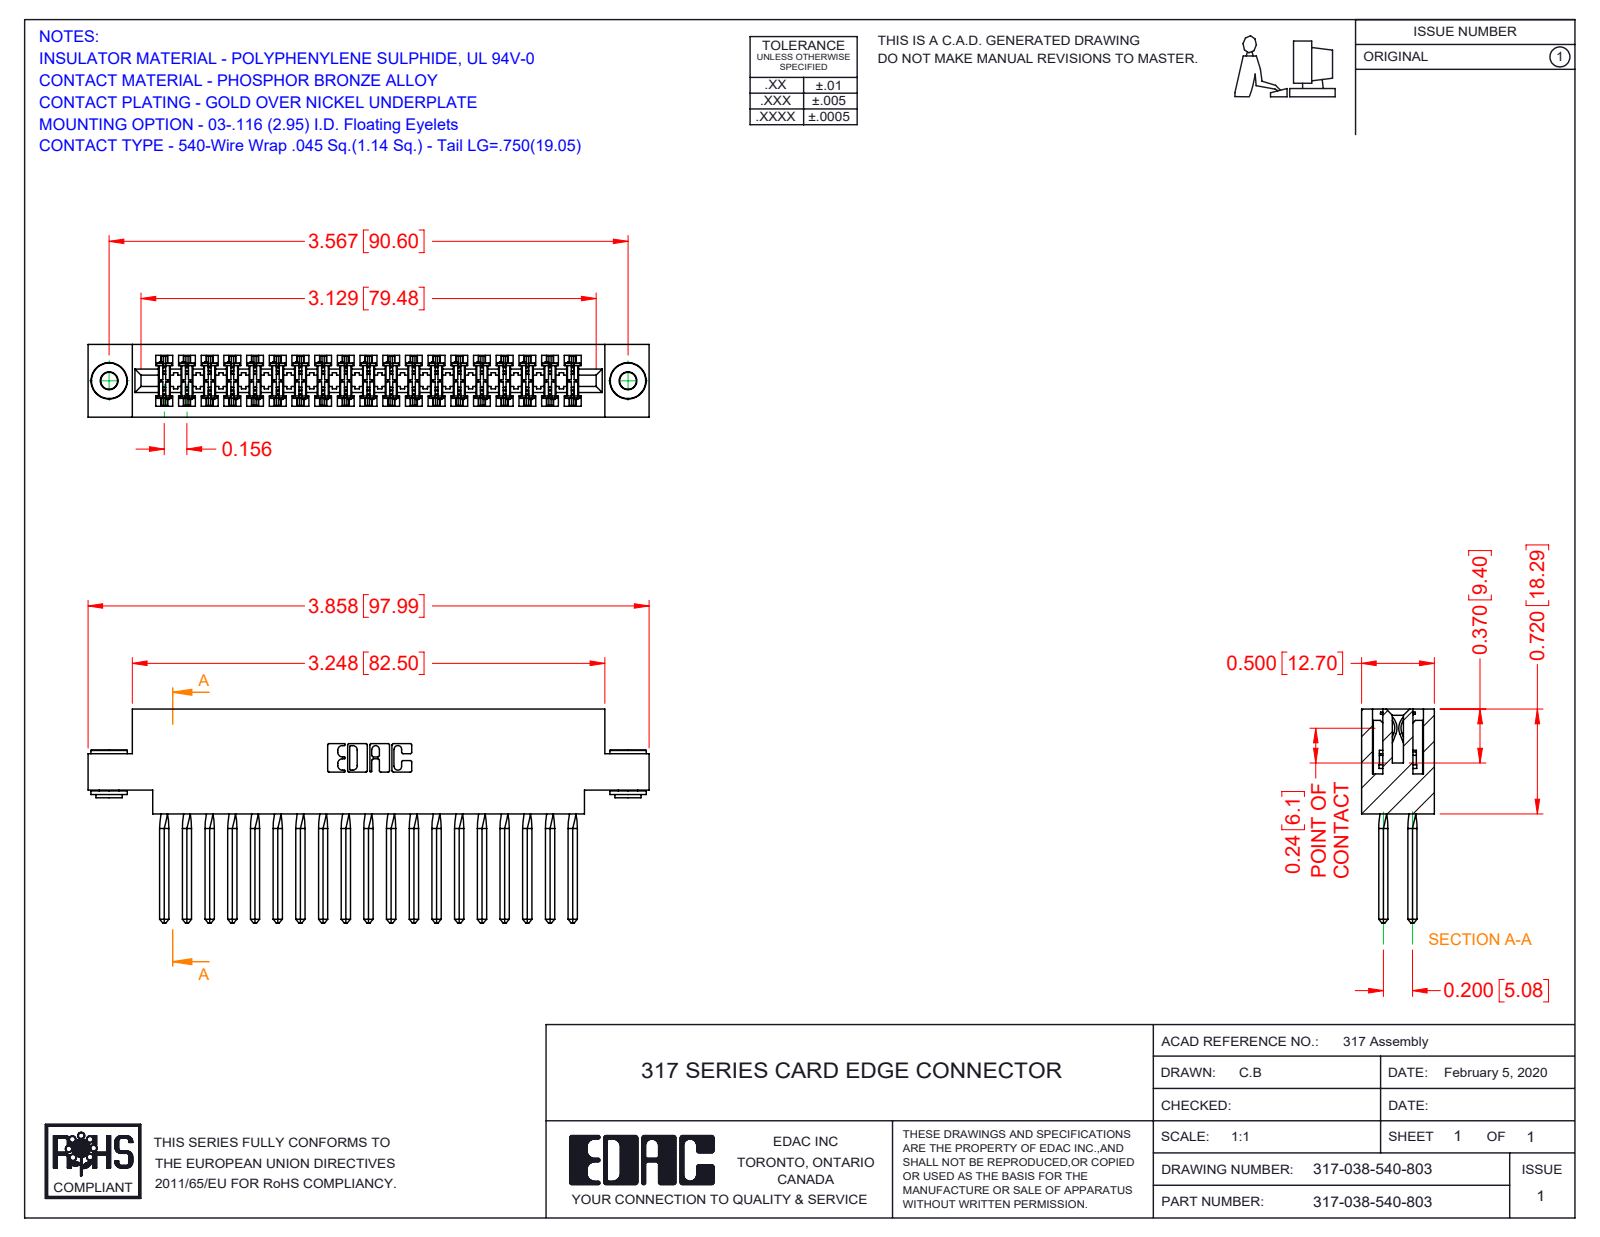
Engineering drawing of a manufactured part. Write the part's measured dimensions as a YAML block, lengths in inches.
part_name: "317 Part_.156 Dia - TH; 317-038-540-803; 317-290-001_540; 345-250-002_345-250-002-102"
step_written_by: "SolidWorks 2016 (CONFIG_CONTROL_DESIGN)"
units: inches
bodies: {solids: 41, faces: 3522, planar: 2842, cylindrical: 520, other: 160}
overall_size: [3.858, 1.47, 0.5]
volume: 0.957
surface_area: 35.24
round_holes:
  - {diameter: 0.116, count: 2}
  - {diameter: 0.156, count: 2}
round_bosses_or_shafts:
  - {diameter: 0.25, count: 2}
  - {diameter: 0.18, count: 2}
  - {diameter: 0.136, count: 2}
partial_cylinders:
  - {radius: 0.015, count: 76}
  - {radius: 0.01, count: 22}
  - {radius: 0.007, count: 6}
  - {radius: 0.031, count: 6}
  - {radius: 0.026, count: 3}
  - {radius: 0.095, count: 2}
  - {radius: 0.1, count: 2}
  - {radius: 0.11, count: 2}
face_to_face_distances: [0.5, 0.075, 0.425, 0.11, 0.35, 0.195, 0.22, 0.72, 0.094, 0.2]
hole_center_spacings: [3.567]
